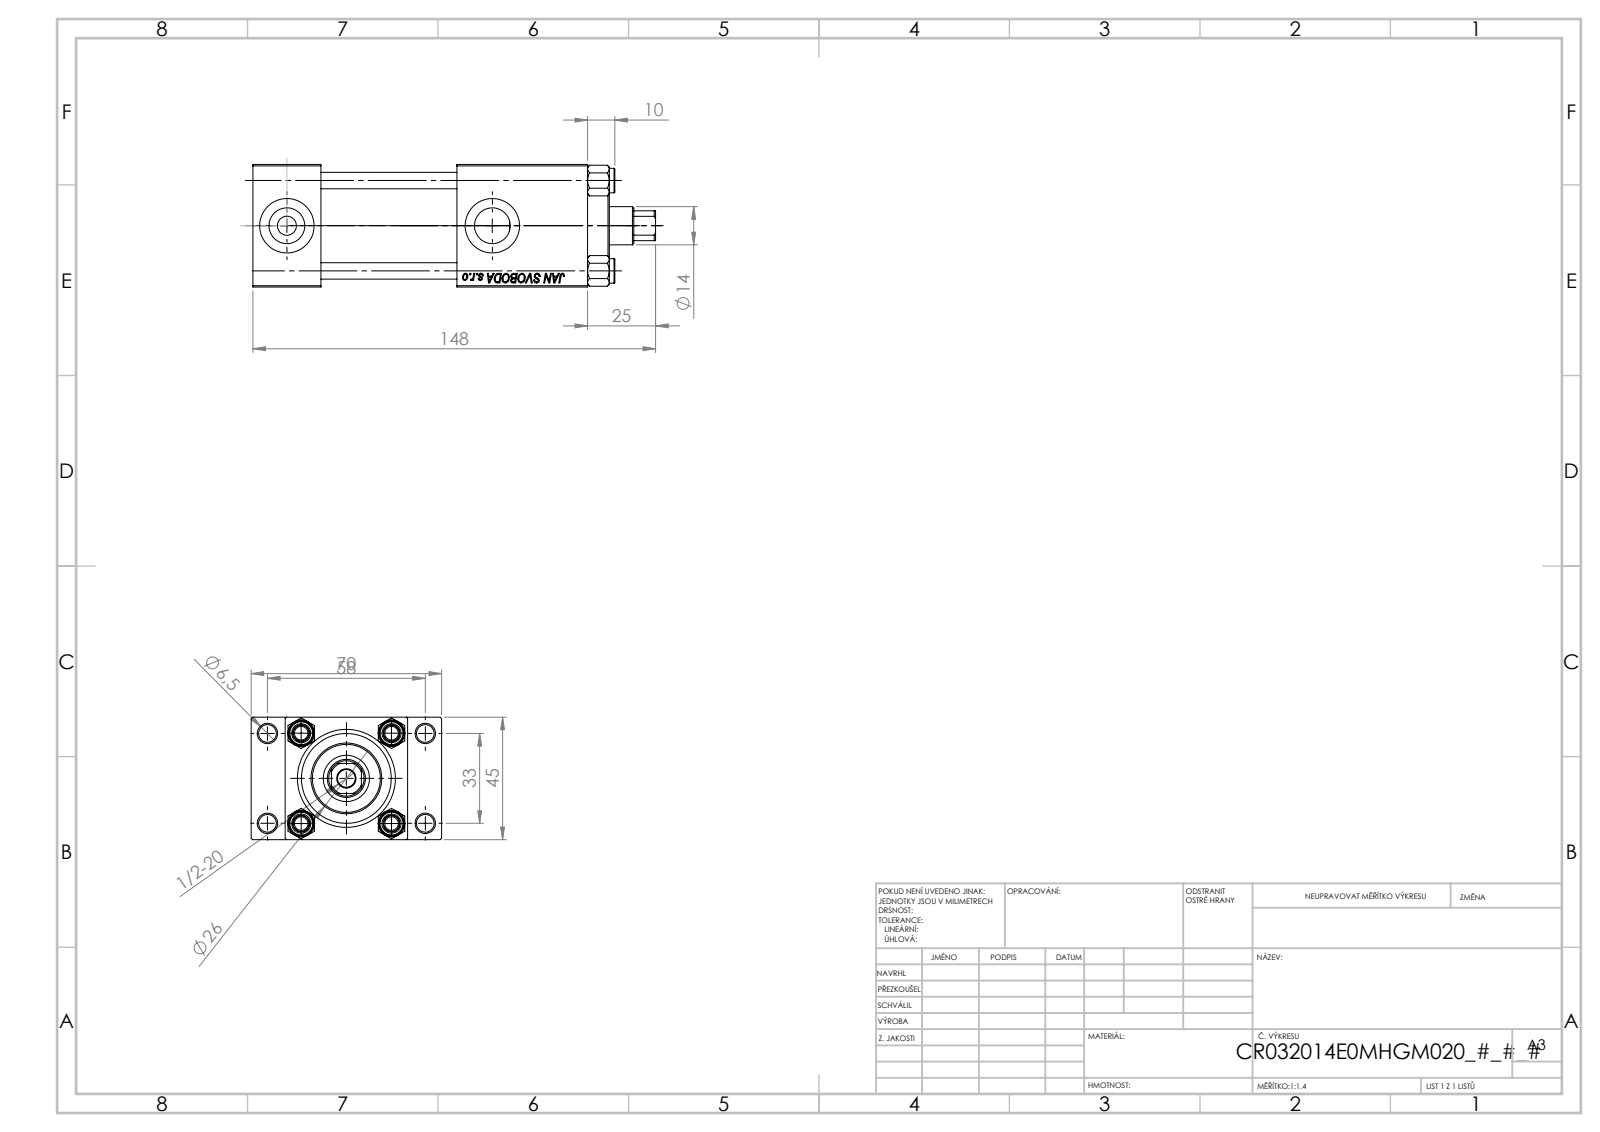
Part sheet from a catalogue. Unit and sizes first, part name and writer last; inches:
Units: inches
Overall size (bounding box): 5.827 × 2.756 × 1.772
Round holes (diameter × count): ⌀0.256 ×5, ⌀0.236 ×4, ⌀0.276 ×2, ⌀0.518 ×2, ⌀0.787 ×2, ⌀0.551 ×1, ⌀0.669 ×1, ⌀0.945 ×1, ⌀1.26 ×1, ⌀1.299 ×1
Round bosses / shafts (diameter × count): ⌀0.354 ×4, ⌀1.496 ×1, ⌀1.024 ×1
Partial cylindrical surfaces — rounded edges, fillets, slot ends (radius × count): R0.256 ×1
Main face-to-face distances: 1.772, 0.984, 0.492, 2.264, 4.843, 3.858, 1.969, 2.953, 1.89, 3.713
Hole centre spacings: 0.488, 0.924, 1.307, 1.314, 1.392, 1.795, 2.219, 1.299
Volume: 13.41 in³ · Surface area: 118.3 in²
Bodies: 11 solids, 1135 faces (497 planar, 86 cylindrical, 552 other)
Part name (STEP PRODUCT): NUT_M5_E; V215CR_E_Body; V215_VC_A; V215CR_TYCINKA_E (+1 more)
STEP written by: SolidWorks 2019 (CONFIG_CONTROL_DESIGN)
